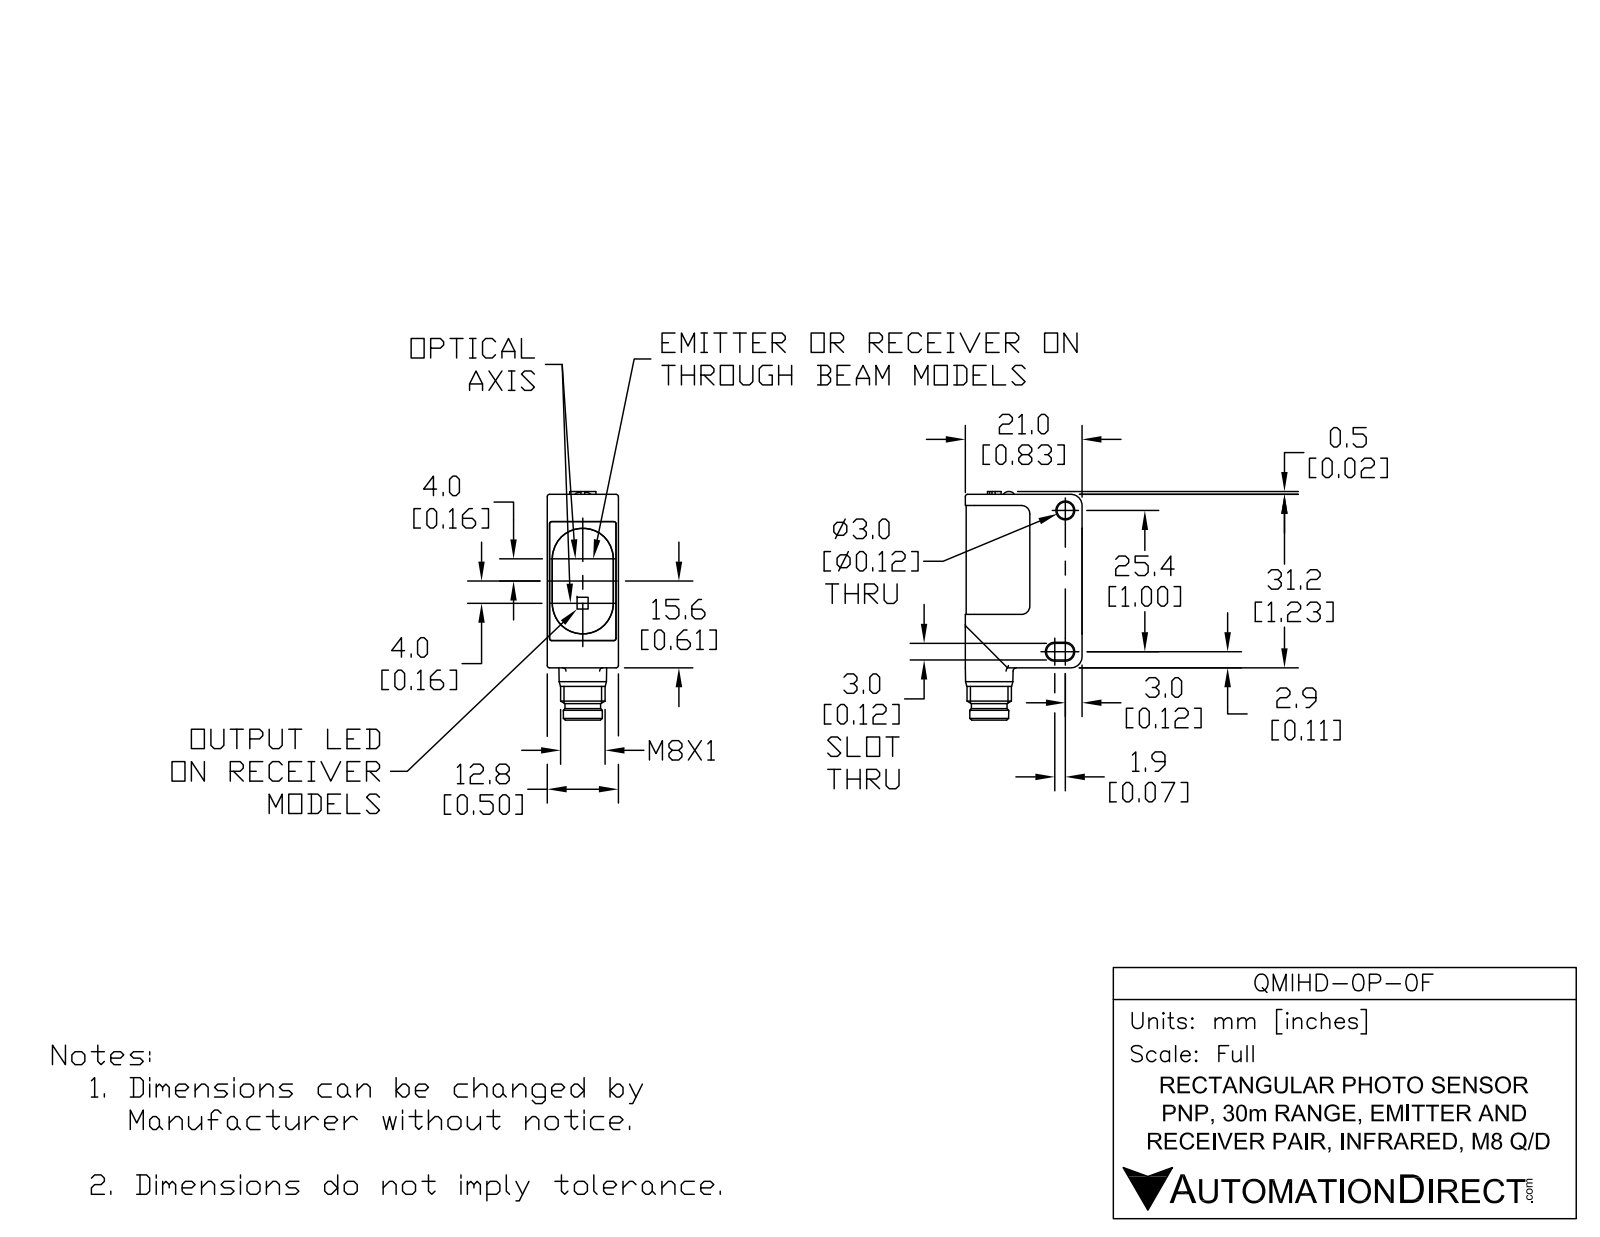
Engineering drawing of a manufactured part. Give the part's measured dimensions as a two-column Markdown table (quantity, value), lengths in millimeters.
| quantity | value |
| --- | --- |
| part name | QMIHD-0P-0F |
| STEP written by | SolidWorks 2017 (AUTOMOTIVE_DESIGN) |
| units | millimeters |
| bodies | 6 solids, 250 faces (114 planar, 89 cylindrical, 47 other) |
| overall size | 41.1 × 21 × 12.8 |
| volume | 7 750 mm³ |
| surface area | 4 974 mm² |
| round holes (diameter × count) | 3 × 2, 5.8 × 1 |
| round bosses / shafts (diameter × count) | 1 × 4, 8 × 1, 7 × 1, 6.4 × 1, 3.5 × 1 |
| partial cylindrical surfaces (radius × count) | 0.4 × 10, 1.5 × 6, 0.5 × 5, 0.6 × 4, 1 × 4, 1.7 × 2, 2 × 2, 5.5 × 2 |
| main face-to-face distances | 12.6, 0.5, 12.8, 2.8, 0.4, 12.5, 12.4, 12.2, 1.5, 18.1 |
| hole center spacings | 1 |
